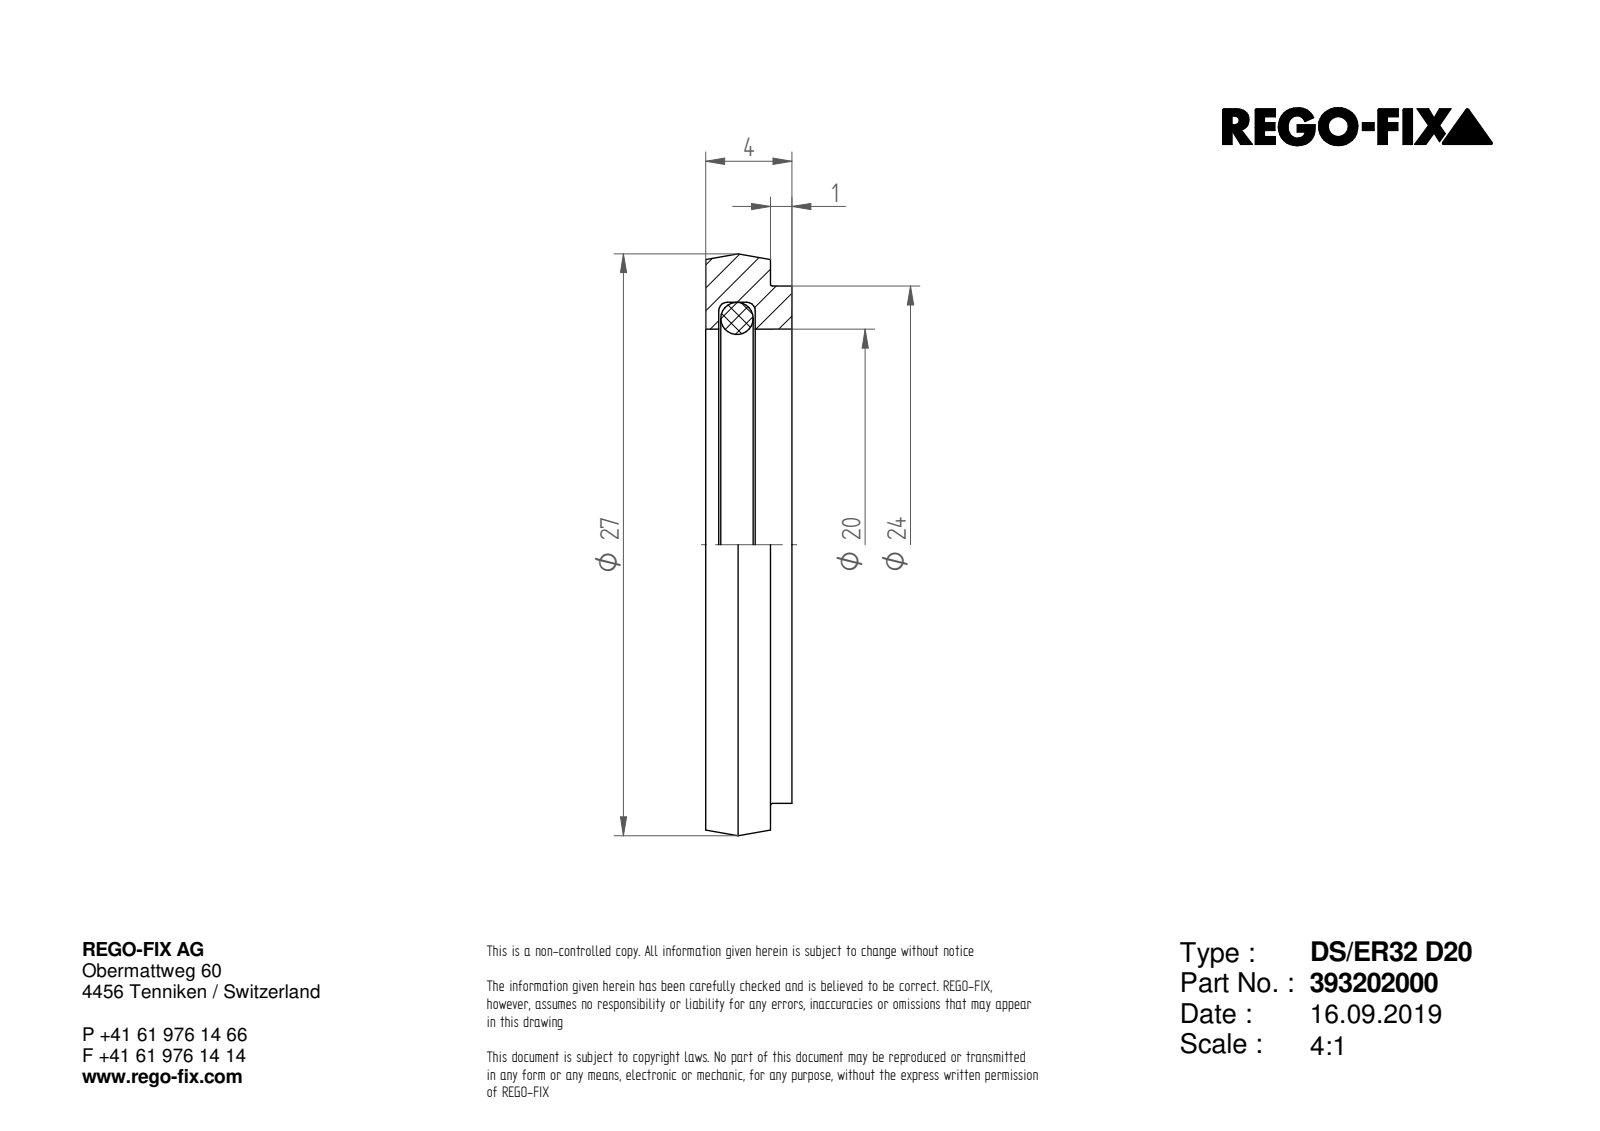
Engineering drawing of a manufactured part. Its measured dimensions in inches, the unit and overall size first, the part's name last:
Units: inches
Overall size (bounding box): 1.063 × 1.063 × 0.157
Round holes (diameter × count): ⌀0.787 ×1
Round bosses / shafts (diameter × count): ⌀1.063 ×1, ⌀0.945 ×1
Main face-to-face distances: 0.157, 0.039, 0.118
Volume: 0.056 in³ · Surface area: 1.697 in²
Bodies: 1 solid, 7 faces (3 planar, 3 cylindrical, 1 other)
Part name (STEP PRODUCT): NOCUT
STEP written by: SIEMENS PLM Software Solid Edge ST10 (AUTOMOTIVE_DESIGN)
